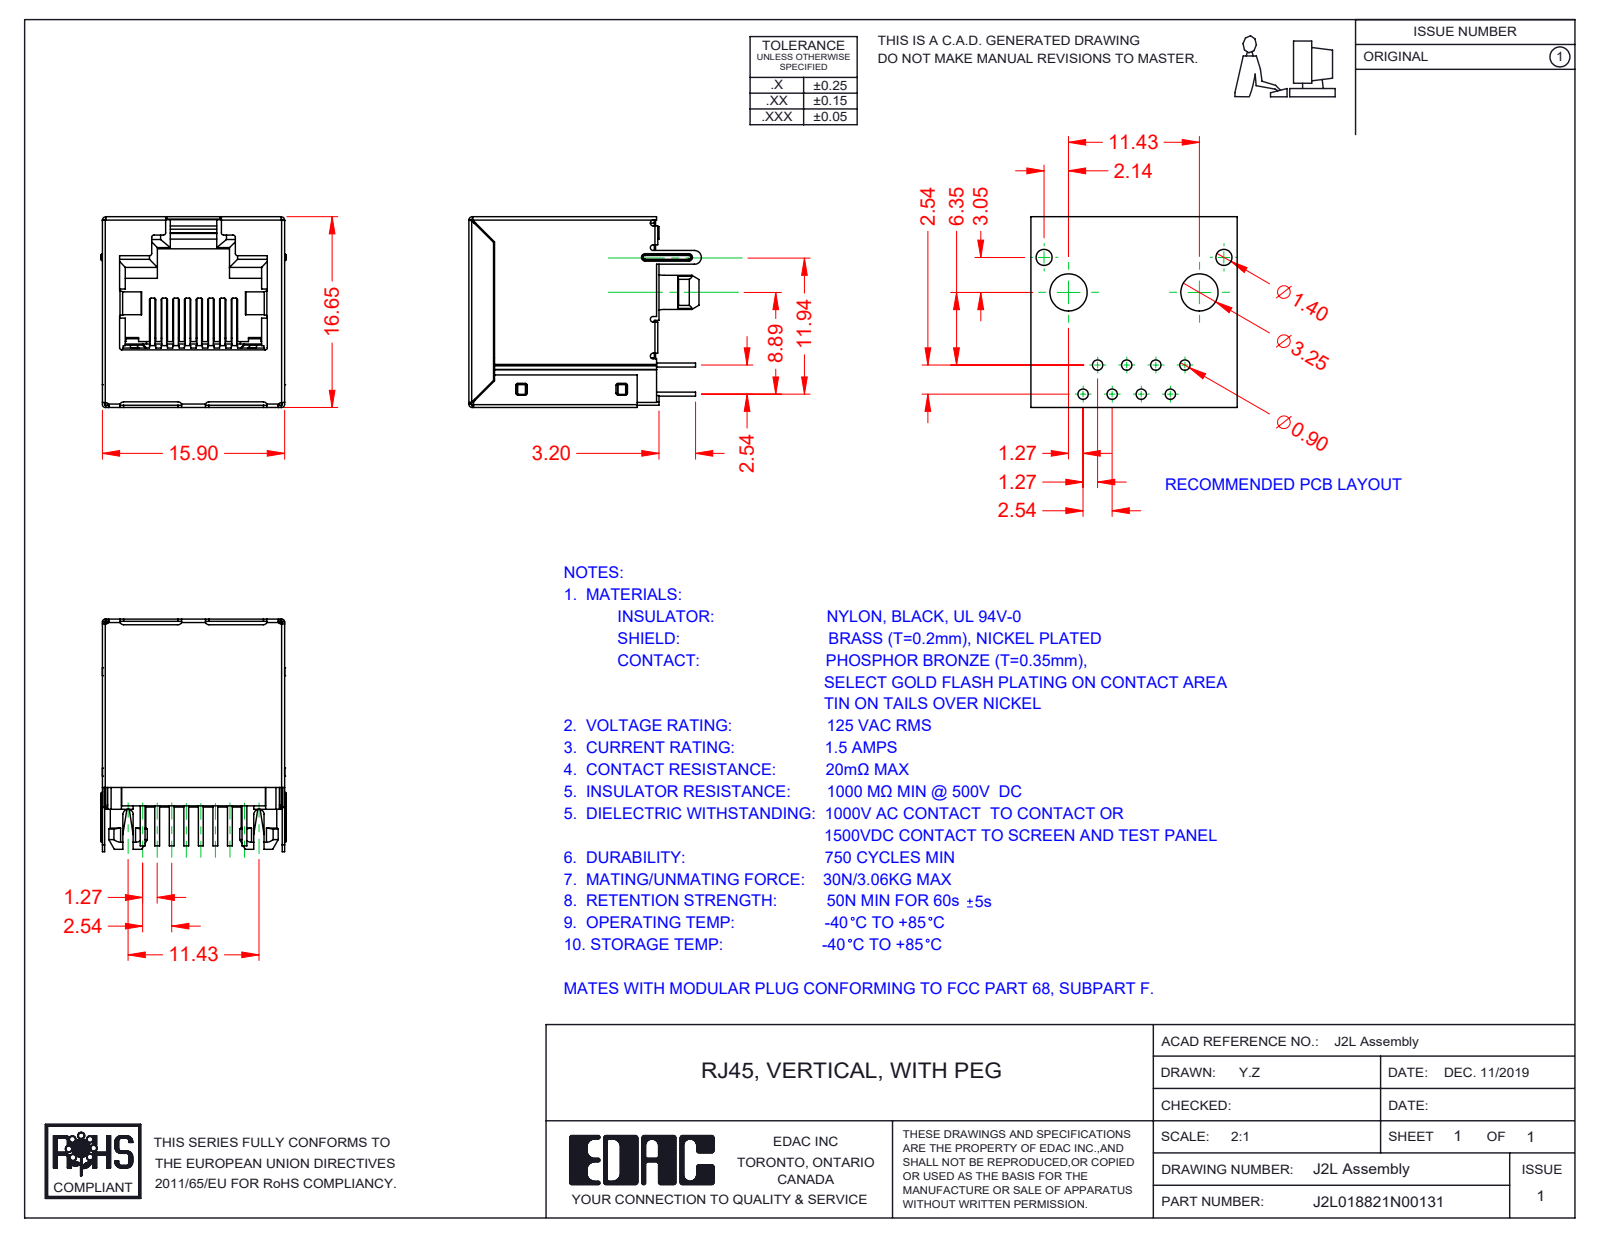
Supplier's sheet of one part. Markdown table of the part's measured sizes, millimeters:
| quantity | value |
| --- | --- |
| part name | 2L Contacts; 2L Contact Lock; 2L Insulator; RJ2L018821N00131 (+1 more) |
| STEP written by | SolidWorks 2016 (CONFIG_CONTROL_DESIGN) |
| units | millimeters |
| bodies | 11 solids, 1125 faces (778 planar, 284 cylindrical, 63 other) |
| overall size | 20.3 × 16.65 × 16.2 |
| volume | 2 717 mm³ |
| surface area | 6 473 mm² |
| round bosses / shafts (diameter × count) | 3.1 × 2, 1.1 × 2 |
| partial cylindrical surfaces (radius × count) | 0.15 × 64, 0.25 × 20, 0.2 × 16, 0.3 × 14, 0.35 × 9, 0.1 × 8, 0.28 × 4, 0.5 × 3 |
| main face-to-face distances | 15.45, 15.7, 16.45, 16.2, 16.4, 15.65, 16.25, 15.9, 15.5, 1.2 |
